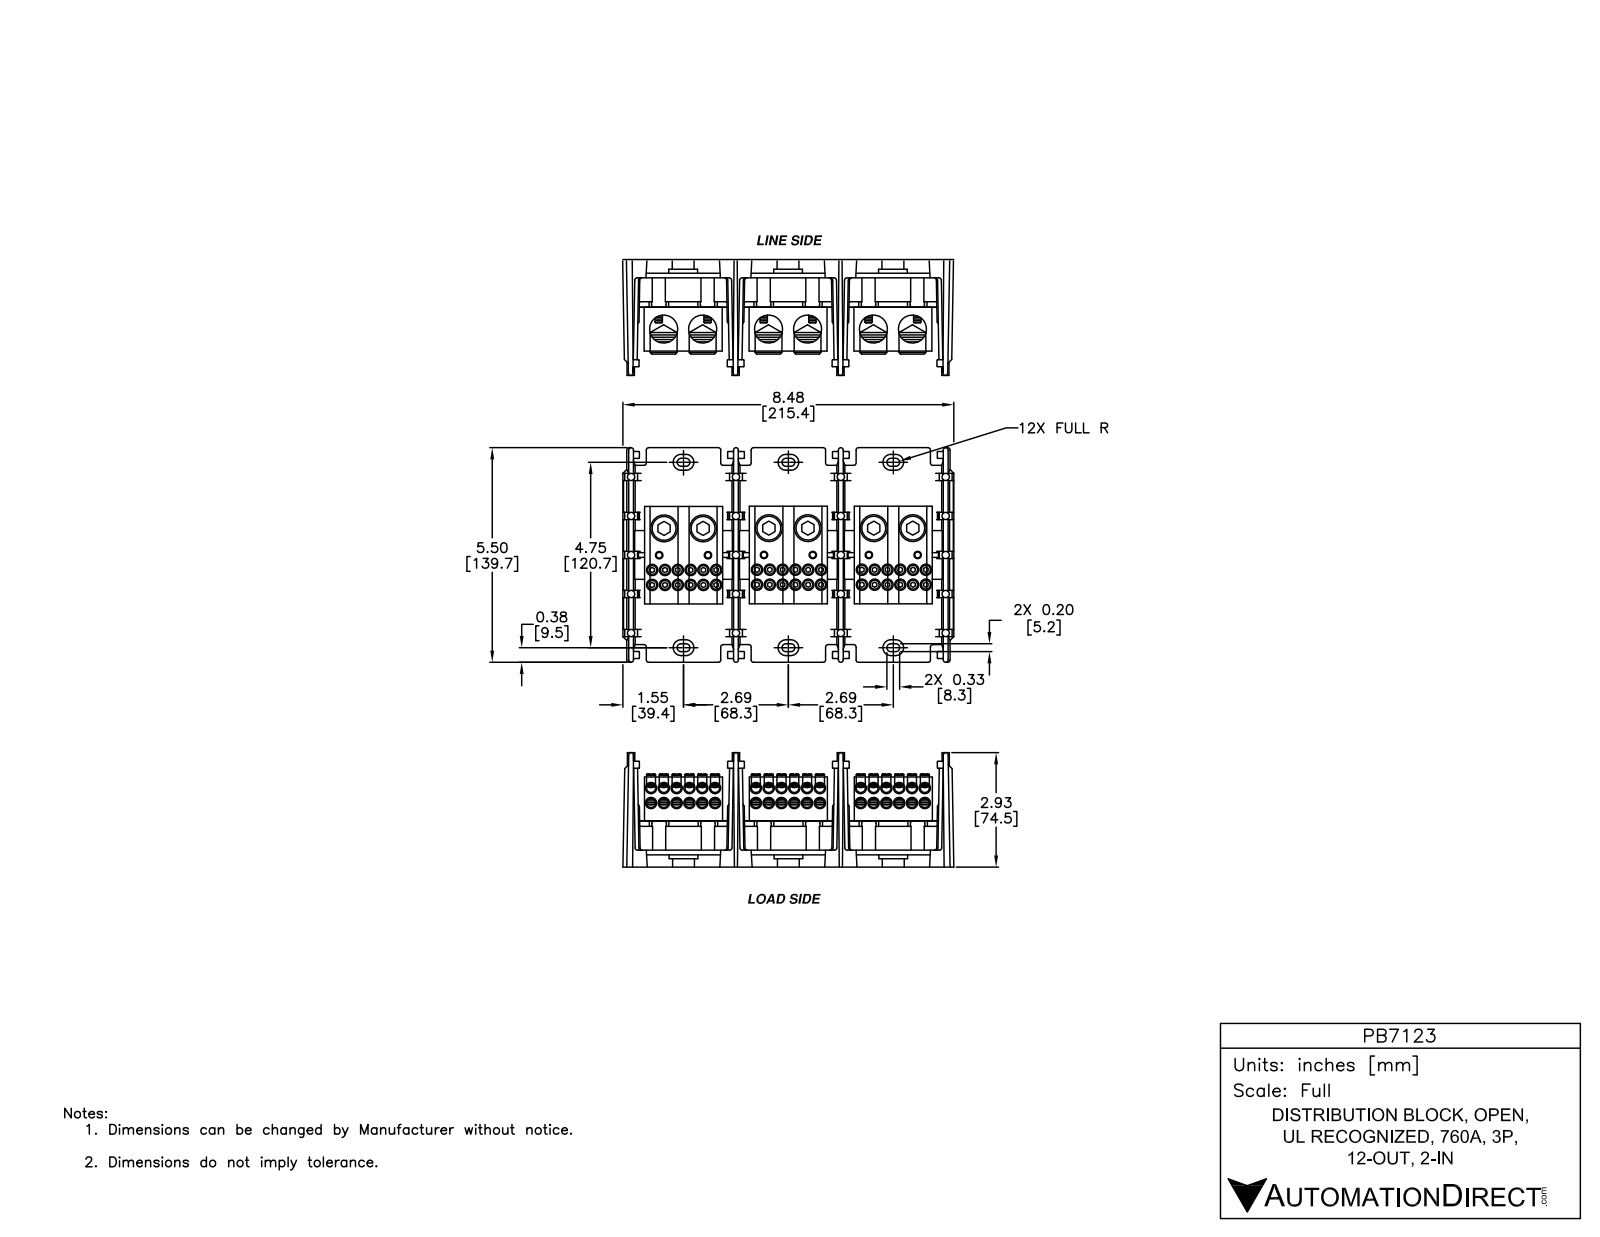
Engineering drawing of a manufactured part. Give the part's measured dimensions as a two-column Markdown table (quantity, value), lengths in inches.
| quantity | value |
| --- | --- |
| part name | PB7123 |
| STEP written by | SolidWorks 2014 (AUTOMOTIVE_DESIGN) |
| units | inches |
| bodies | 60 solids, 2039 faces (1217 planar, 718 cylindrical, 104 other) |
| overall size | 8.484 × 5.484 × 2.922 |
| volume | 34.5 in³ |
| surface area | 541.6 in² |
| round holes (diameter × count) | 0.25 × 42, 0.219 × 36, 0.175 × 22, 0.375 × 6, 0.75 × 6, 0.875 × 6 |
| round bosses / shafts (diameter × count) | 0.625 × 6, 0.187 × 2 |
| partial cylindrical surfaces (radius × count) | 0.097 × 12, 0.2 × 12, 0.203 × 12, 0.1 × 10, 0.313 × 10, 0.031 × 8, 0.312 × 2 |
| main face-to-face distances | 2.703, 5.406, 2.703, 0.125, 2.58, 0.123, 0.249, 2.826, 5.529, 8.109 |
| hole center spacings | 1, 2.703, 2.882, 0.586, 0.75, 0.875, 2, 3.363 |
